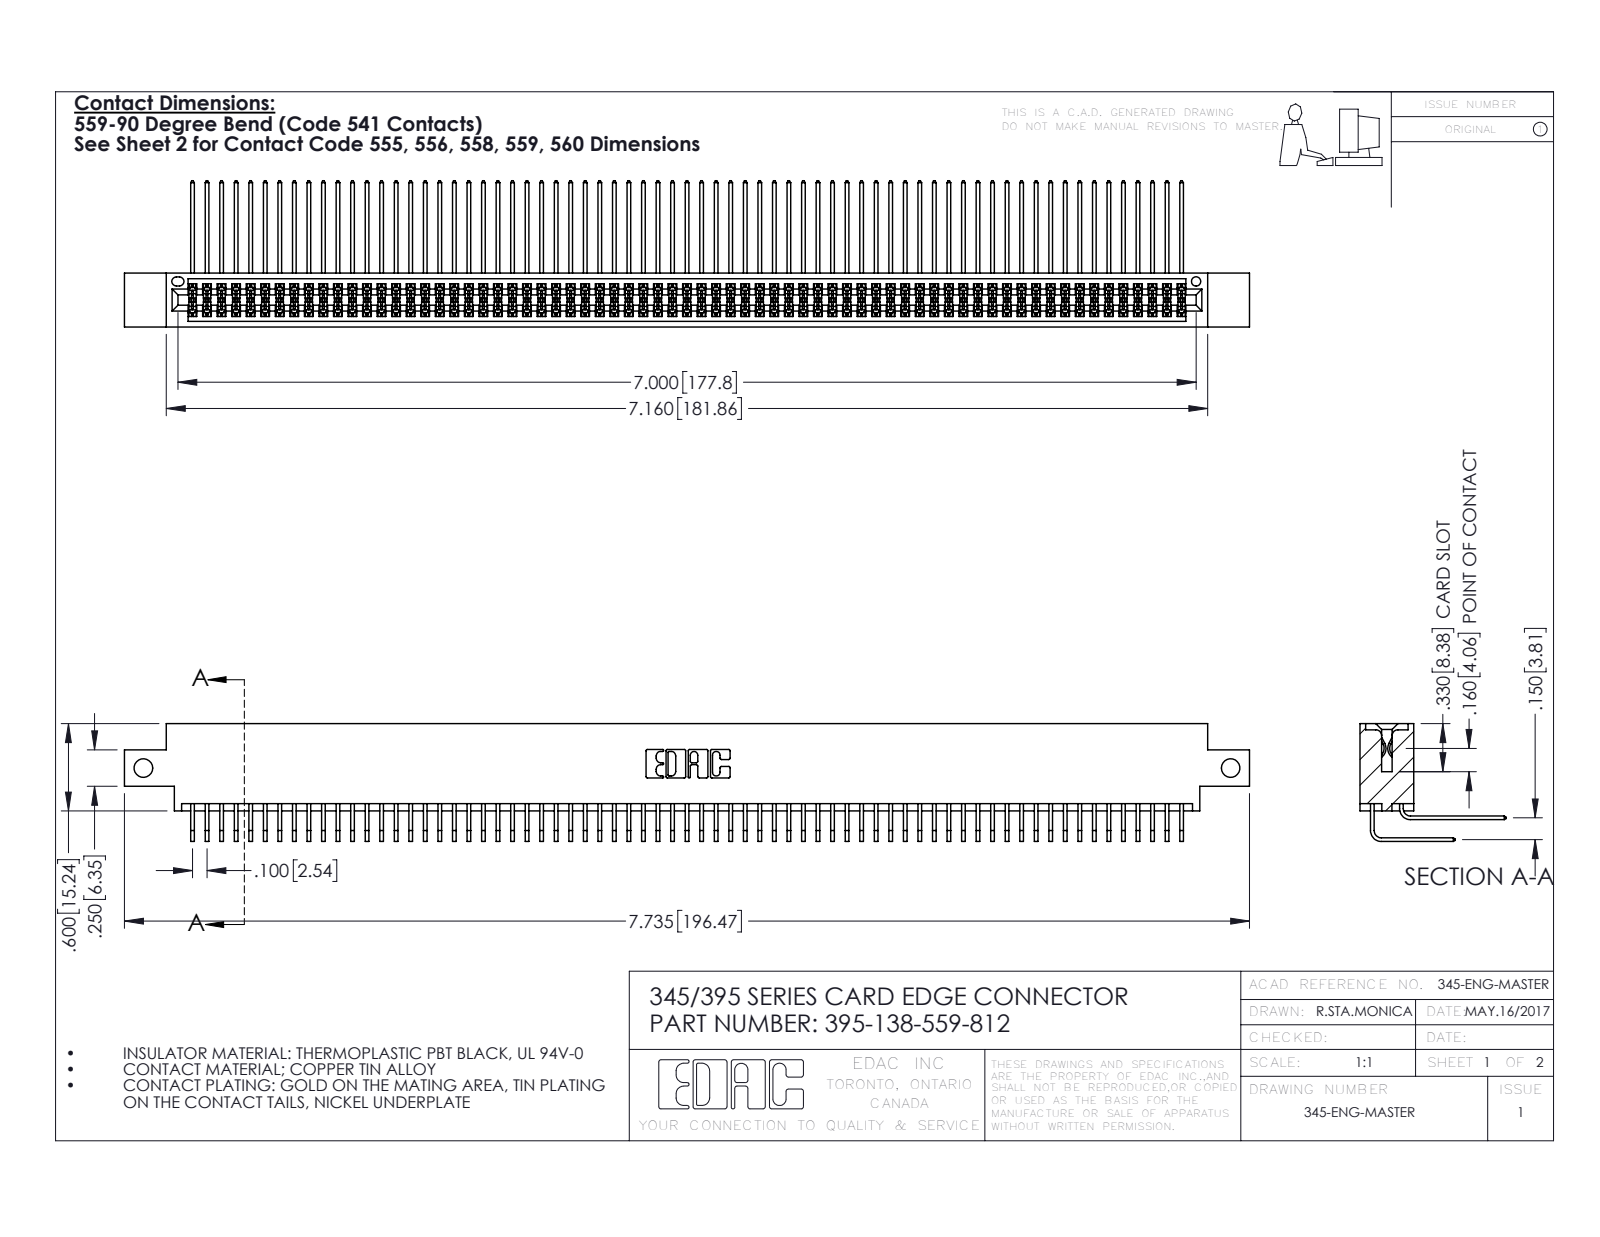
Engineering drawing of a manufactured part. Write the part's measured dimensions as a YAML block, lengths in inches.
part_name: "345 Part_0.170 Offset - Side Mount; 395-138-559-812; 345-292-001_558 559 Tail - 1; 345-292-001_559 Tail - 2"
step_written_by: "SolidWorks 2016 (CONFIG_CONTROL_DESIGN)"
units: inches
bodies: {solids: 139, faces: 7306, planar: 4914, cylindrical: 2392, other: 0}
overall_size: [7.735, 1.005, 0.809]
volume: 1.216
surface_area: 52.29
round_holes:
  - {diameter: 0.128, count: 2}
  - {diameter: 0.064, count: 1}
partial_cylinders:
  - {radius: 0.006, count: 275}
  - {radius: 0.01, count: 22}
  - {radius: 0.007, count: 6}
  - {radius: 0.031, count: 6}
  - {radius: 0.026, count: 3}
  - {radius: 0.014, count: 2}
  - {radius: 0.019, count: 2}
  - {radius: 0.022, count: 2}
face_to_face_distances: [0.072, 0.298, 0.37, 0.2, 0.098, 0.272, 0.025, 0.225, 0.175, 0.15]
hole_center_spacings: [7.475]
